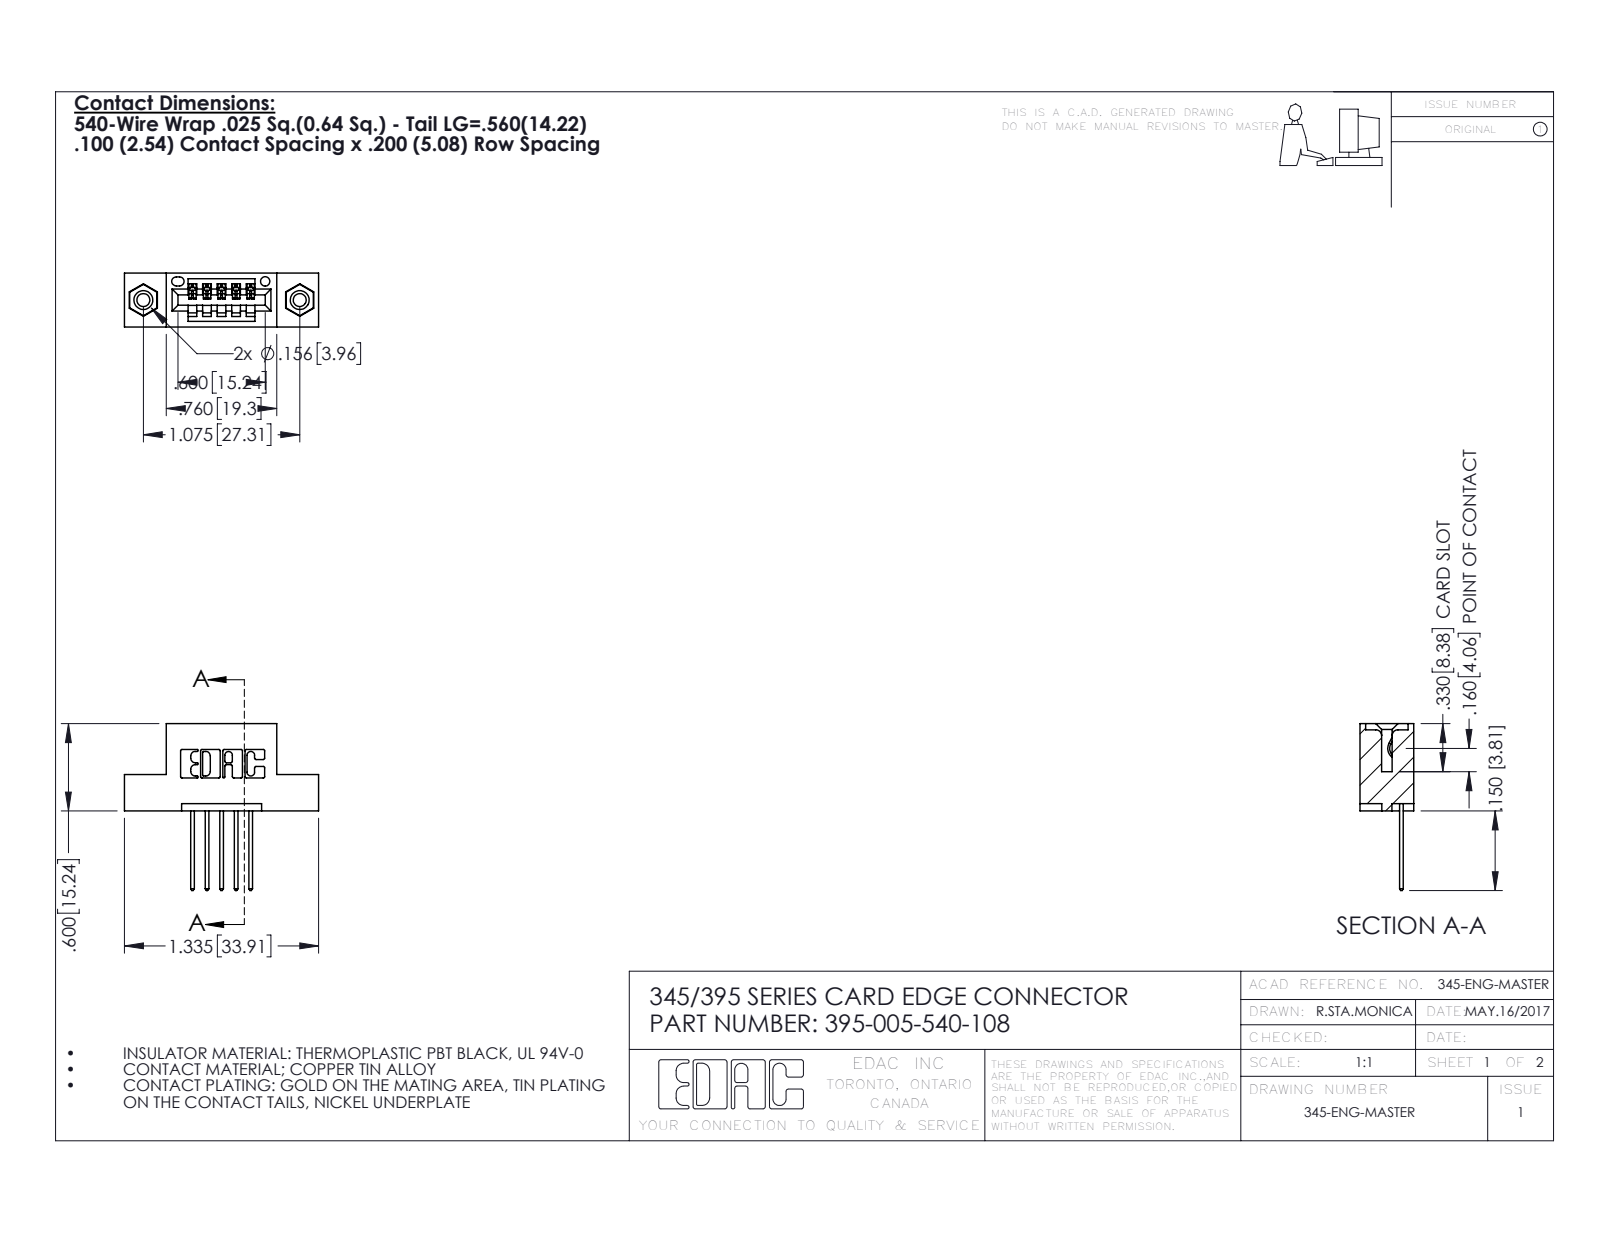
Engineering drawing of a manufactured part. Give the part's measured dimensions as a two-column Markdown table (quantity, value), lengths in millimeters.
| quantity | value |
| --- | --- |
| part name | 345-292-001_345-293-140; 345-250-001_345-250-003-102; 395-005-540-108; 345 Part_Flush Mounting Lugs - 0.156 Dia-TI |
| STEP written by | SolidWorks 2016 (CONFIG_CONTROL_DESIGN) |
| units | millimeters |
| bodies | 8 solids, 476 faces (312 planar, 148 cylindrical, 16 other) |
| overall size | 33.9 × 29.1 × 9.4 |
| volume | 2 920 mm³ |
| surface area | 3 443 mm² |
| round holes (diameter × count) | 2.3 × 2, 3.2 × 2, 4 × 2, 1.6 × 1 |
| round bosses / shafts (diameter × count) | 3.9 × 2 |
| partial cylindrical surfaces (radius × count) | 0.3 × 22, 0.2 × 10, 0.3 × 10, 0.2 × 6, 0.8 × 6, 0.7 × 3, 0.8 × 2, 1 × 2 |
| main face-to-face distances | 5.1, 9.4, 1.8, 7.6, 2.5, 0.6, 2.5, 6.9, 8.9, 6.4 |
| hole center spacings | 6.9, 21.5, 27.3 |
